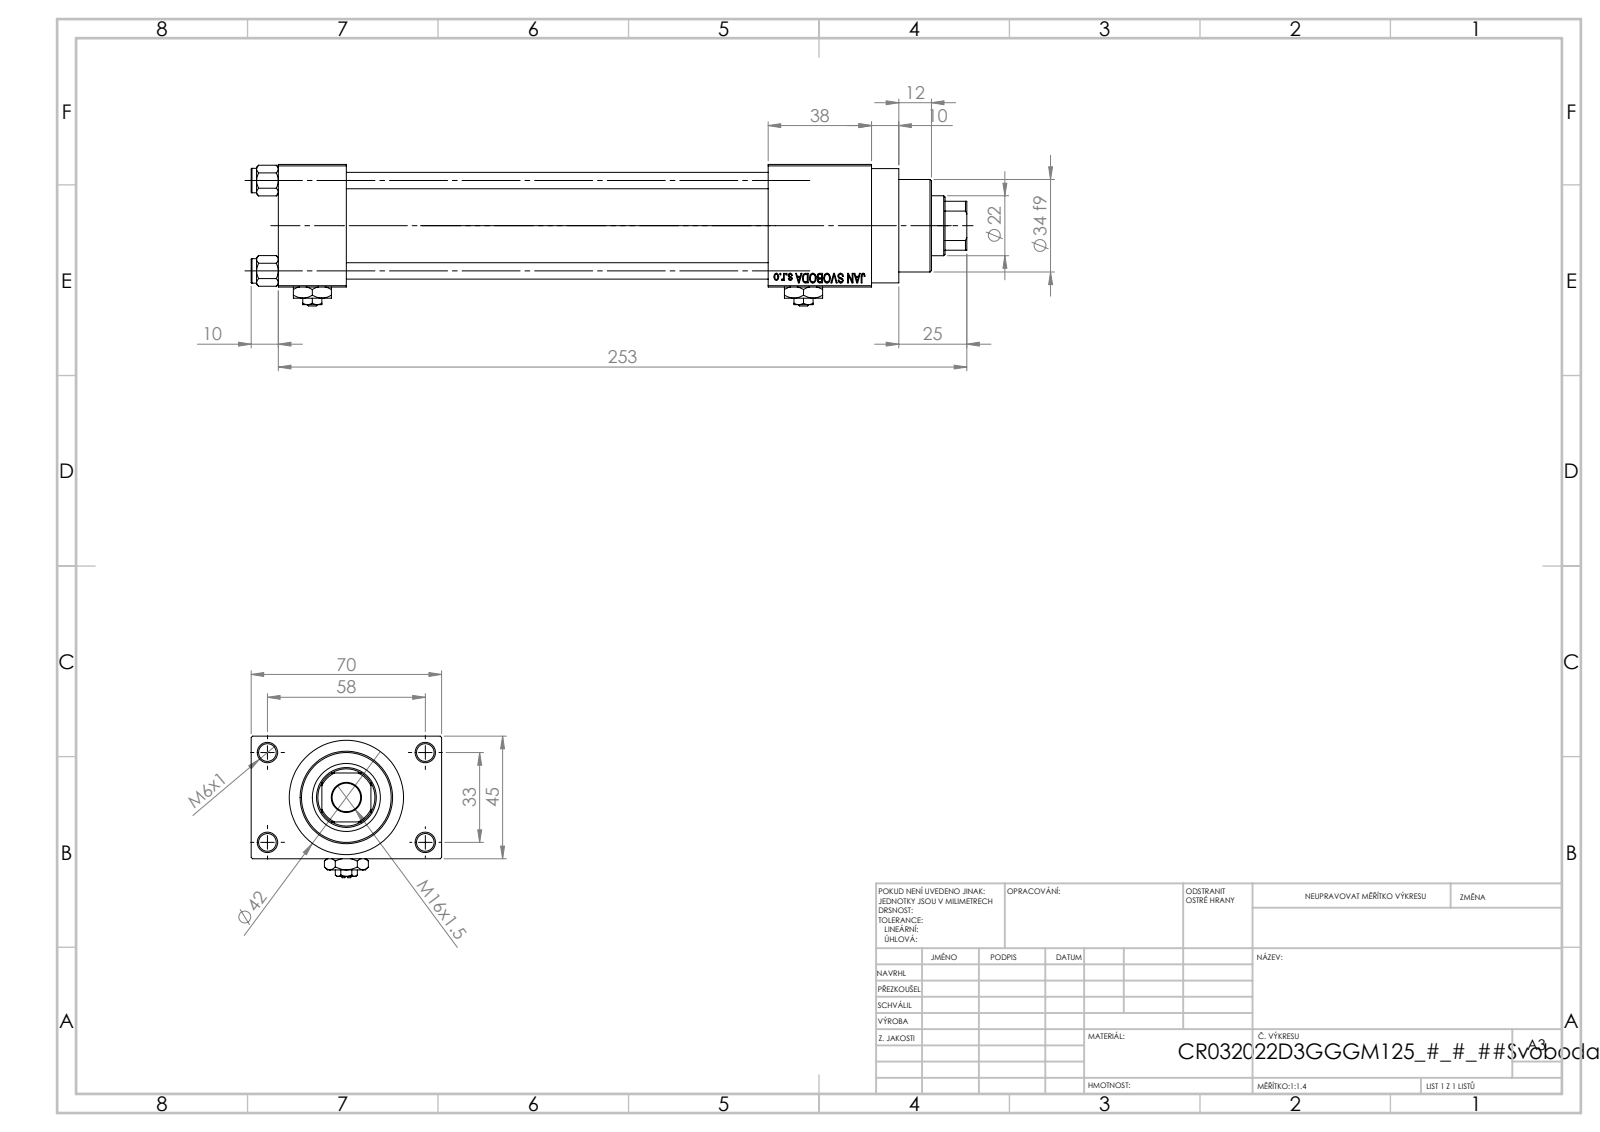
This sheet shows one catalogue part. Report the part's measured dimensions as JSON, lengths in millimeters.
{"part_name": "V215CR_D_TYCINKA; V215CR_D_Body; NUT_M5_D; V215CR_VCP_D (+2 more)", "step_written_by": "SolidWorks 2019 (CONFIG_CONTROL_DESIGN)", "units": "millimeters", "bodies": {"solids": 13, "faces": 1202, "planar": 542, "cylindrical": 100, "other": 560}, "overall_size": [263, 70, 52], "volume_mm3": 329793, "surface_area_mm2": 119465, "round_holes": [[6, 4], [6.5, 4], [7, 2], [13.16, 2], [20, 2], [10.5, 1], [22, 1], [24, 1], [25, 1], [32, 1], [33, 1]], "round_bosses_or_shafts": [[9, 4], [42, 1], [38, 1], [34, 1]], "partial_cylinders_radius": [[10.5, 1]], "face_to_face_distances": [45, 25, 12.5, 57.5, 155, 180, 193, 38, 70, 218], "hole_center_spacings": [12.4, 23.48, 33.2, 33.37, 35.35, 45.6, 56.35, 33]}
